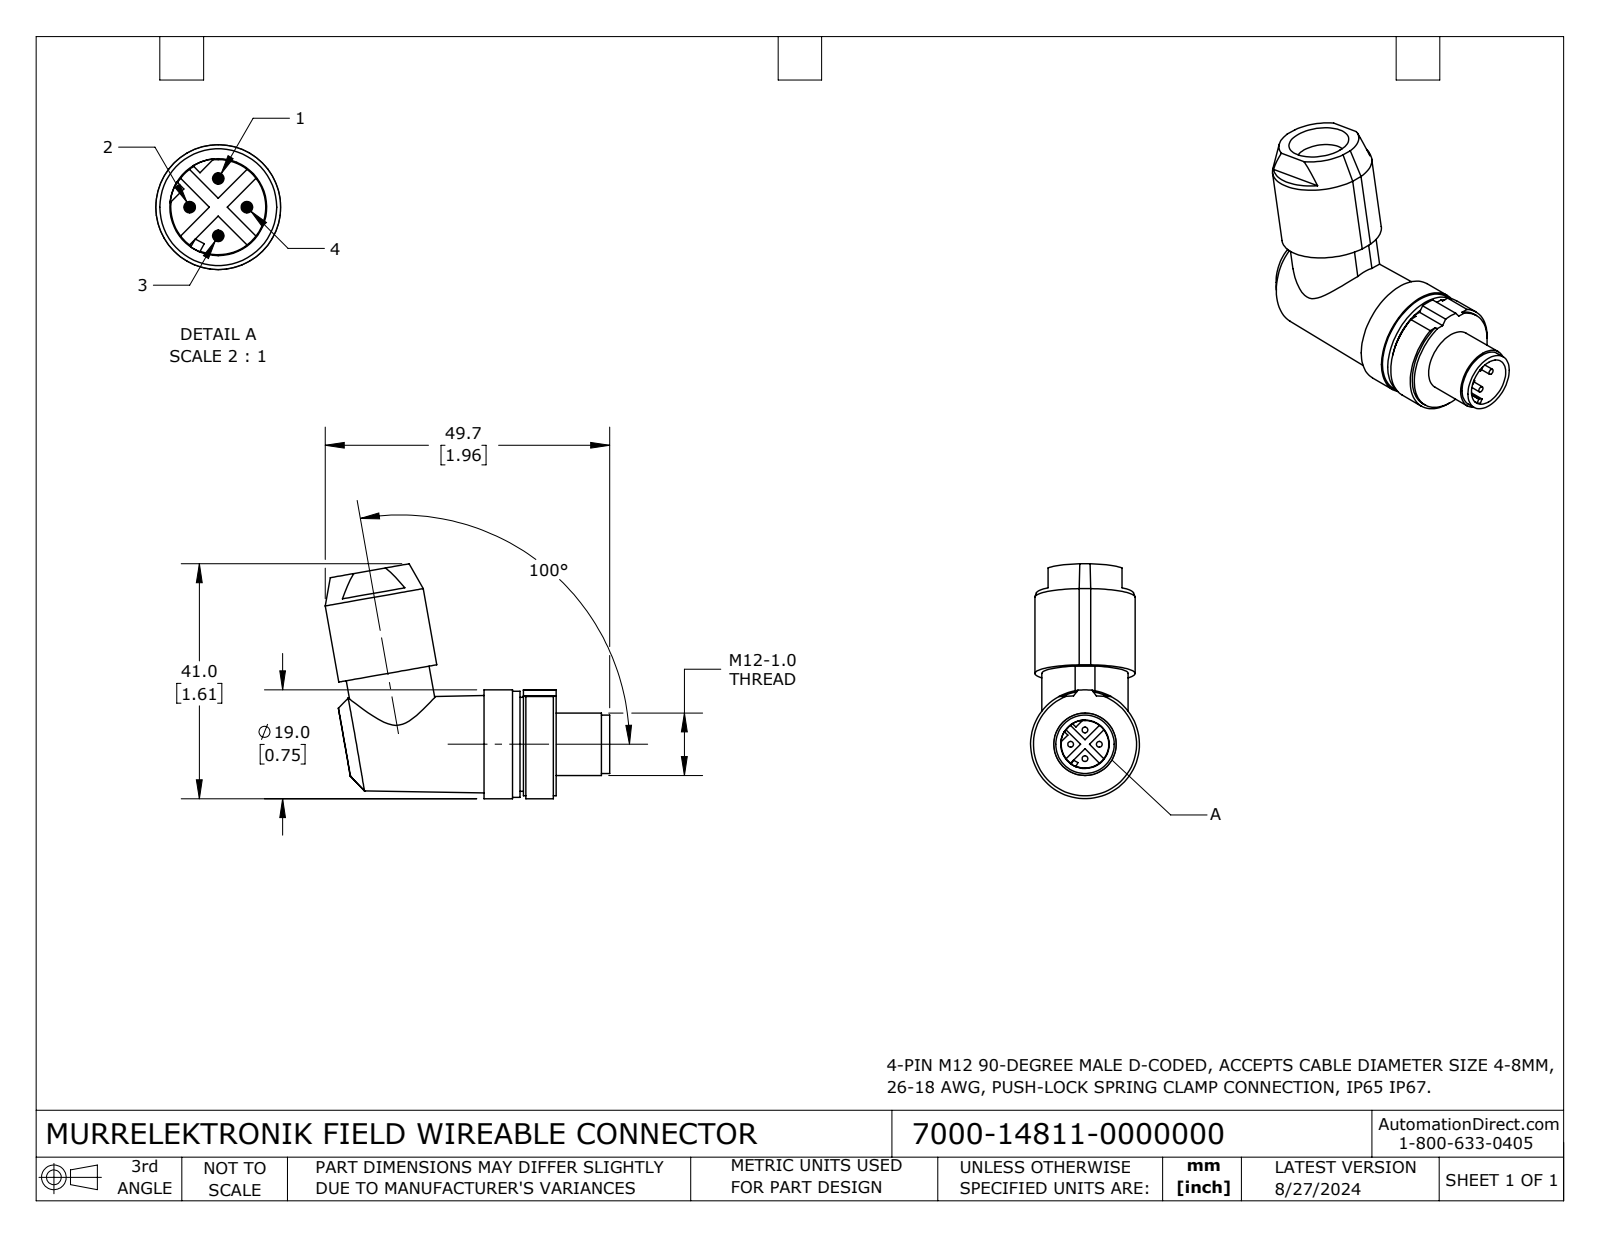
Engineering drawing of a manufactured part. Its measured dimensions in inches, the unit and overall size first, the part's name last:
Units: inches
Overall size (bounding box): 1.955 × 1.614 × 0.748
Round holes (diameter × count): ⌀0.335 ×1
Round bosses / shafts (diameter × count): ⌀0.039 ×4, ⌀0.748 ×1, ⌀0.728 ×1, ⌀0.709 ×1, ⌀0.689 ×1, ⌀0.646 ×1, ⌀0.594 ×1, ⌀0.429 ×1
Main face-to-face distances: 0.248, 0.717, 0.496, 0.224, 0.024, 0.272, 0.559, 0.018, 0.508, 0.242
Volume: 0.724 in³ · Surface area: 8.699 in²
Bodies: 1 solid, 99 faces (54 planar, 33 cylindrical, 12 other)
Part name (STEP PRODUCT): 7000-14811-0000000
STEP written by: SolidWorks 2023 (CONFIG_CONTROL_DESIGN)
